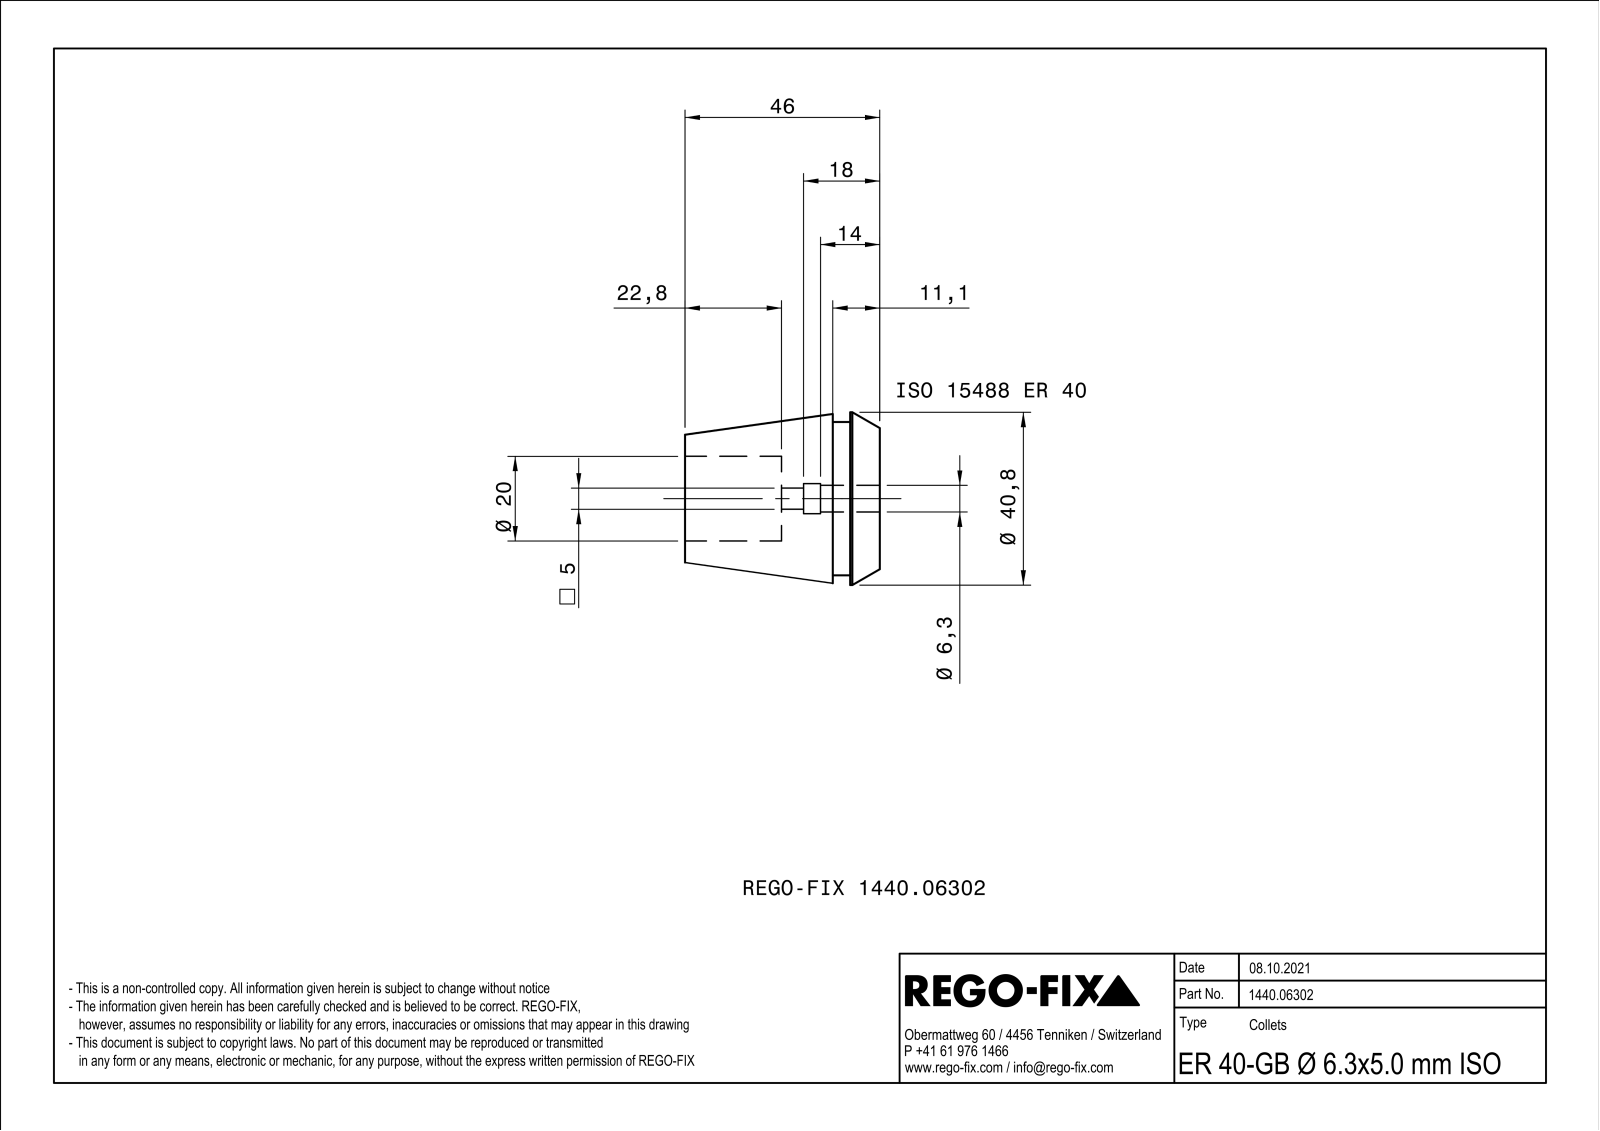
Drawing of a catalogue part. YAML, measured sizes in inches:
part_name: "NOCUT"
step_written_by: "SIEMENS PLM Software Solid Edge ST10 (AUTOMOTIVE_DESIGN)"
units: inches
bodies: {solids: 1, faces: 160, planar: 68, cylindrical: 32, other: 60}
overall_size: [1.811, 1.606, 1.606]
volume: 2.099
surface_area: 24.22
round_holes:
  - {diameter: 0.248, count: 1}
  - {diameter: 0.787, count: 1}
round_bosses_or_shafts:
  - {diameter: 1.606, count: 1}
  - {diameter: 1.425, count: 1}
partial_cylinders:
  - {radius: 0.112, count: 1}
  - {radius: 0.14, count: 1}
face_to_face_distances: [0.039, 1.811, 0.276, 1.535, 0.437, 0.161, 1.374, 0.913, 0.638, 0.476]
